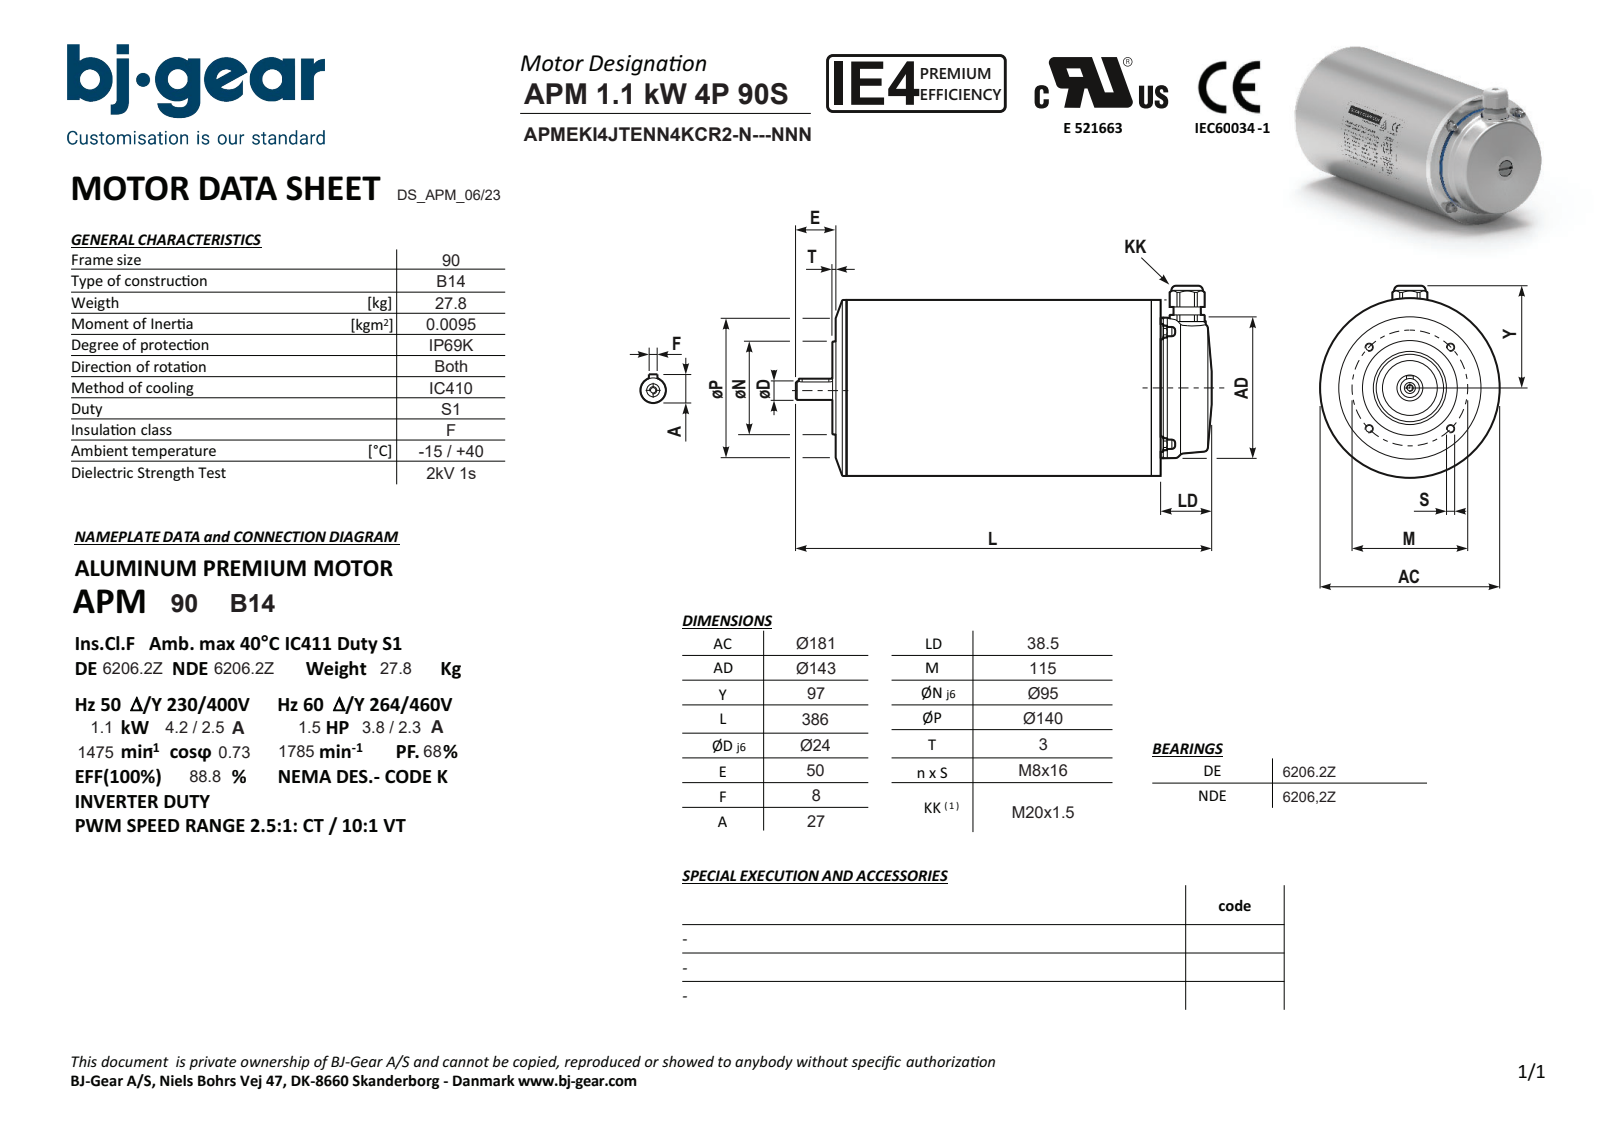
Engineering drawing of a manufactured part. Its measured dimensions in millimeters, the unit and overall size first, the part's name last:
Units: millimetres
Overall size (bounding box): 386 × 187.3 × 182.6
Round holes (diameter × count): ⌀6.65 ×5, ⌀8.4 ×1, ⌀16 ×1, ⌀28 ×1, ⌀82 ×1
Round bosses / shafts (diameter × count): ⌀11.5 ×4, ⌀7 ×4, ⌀182.6 ×1, ⌀182.6 ×1, ⌀143 ×1, ⌀95 ×1, ⌀30 ×1, ⌀24 ×1
Partial cylindrical surfaces — rounded edges, fillets, slot ends (radius × count): R4 ×2, R13.2 ×1
Main face-to-face distances: 297.5, 6, 291.5, 3, 9, 300.5, 8, 336, 38.5, 330
Hole centre spacings: 57.5, 81.32, 115
Volume: 8 327 000 mm³ · Surface area: 247 972 mm²
Bodies: 1 solid, 156 faces (75 planar, 50 cylindrical, 31 other)
Part name (STEP PRODUCT): APMEKI4JTENN4KCR2-N---NNN
STEP written by: Solid Edge (AUTOMOTIVE_DESIGN)
